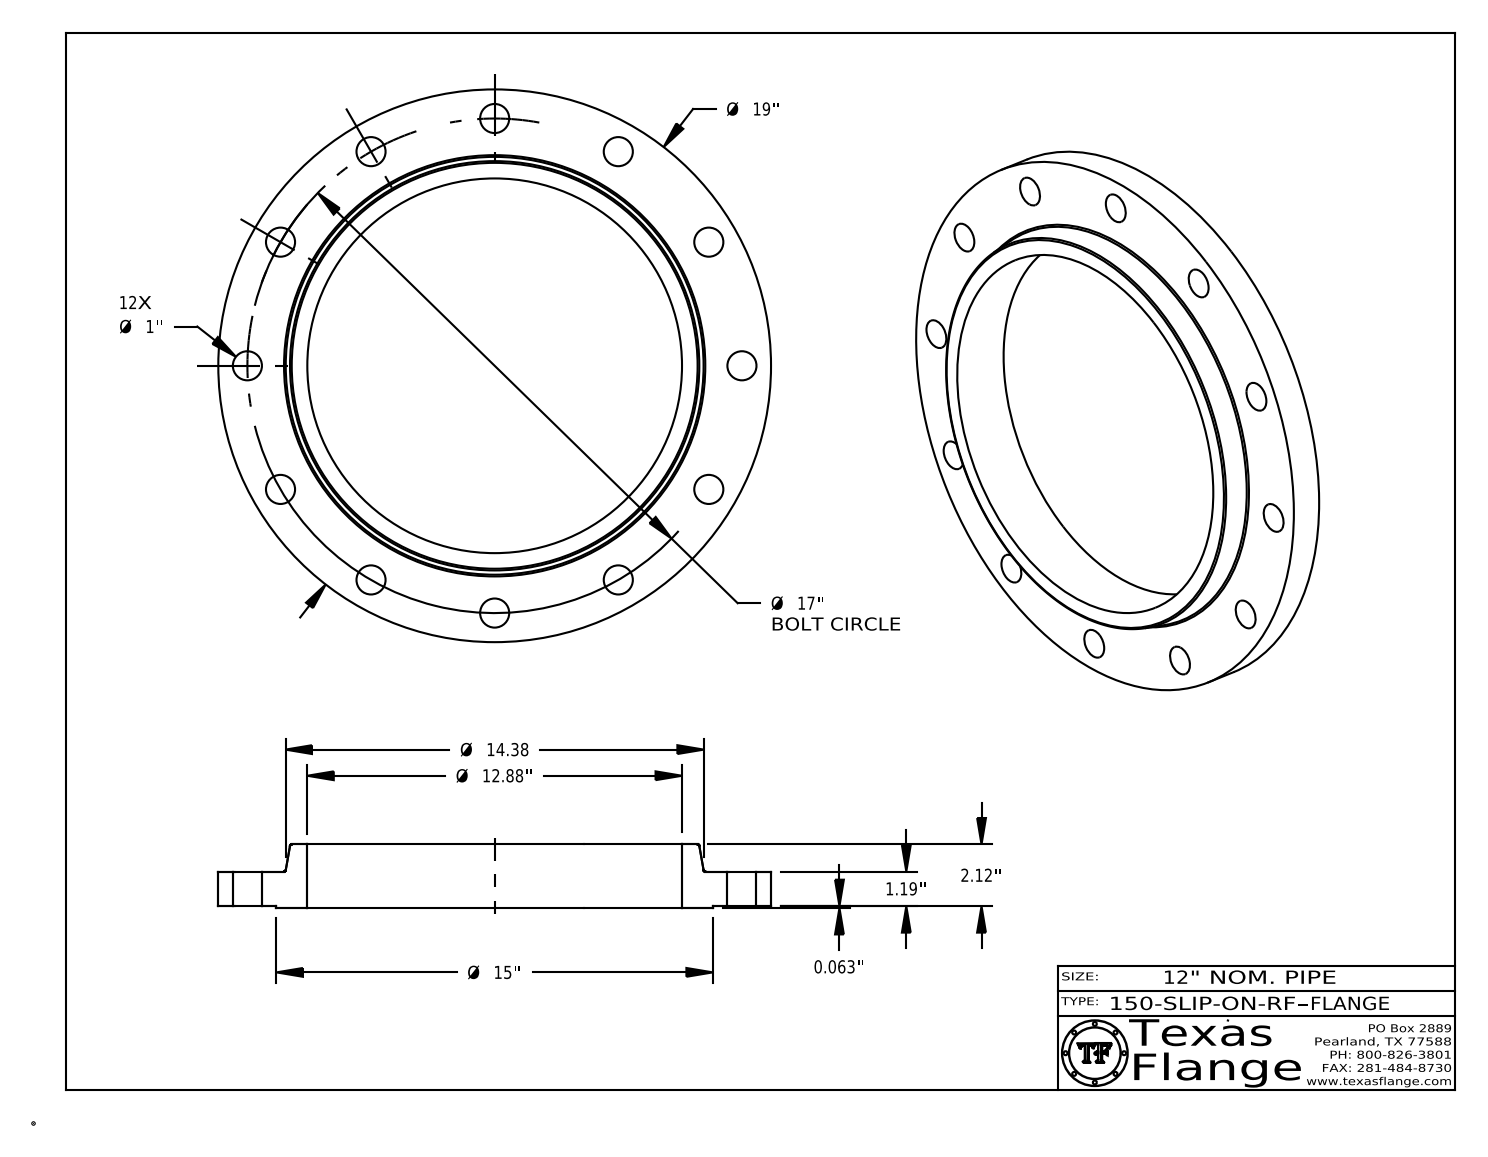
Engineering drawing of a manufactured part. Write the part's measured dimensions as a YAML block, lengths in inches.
part_name: "150-SLIP-ON-RF"
step_written_by: "CATIA V5 STEP AP214 (AUTOMOTIVE_DESIGN)"
units: inches
bodies: {solids: 1, faces: 425, planar: 369, cylindrical: 50, other: 6}
overall_size: [19, 19, 2.183]
volume: 200.5
surface_area: 528.2
round_holes:
  - {diameter: 1, count: 12}
  - {diameter: 0.495, count: 1}
  - {diameter: 12.88, count: 1}
round_bosses_or_shafts:
  - {diameter: 0.03, count: 8}
  - {diameter: 19, count: 1}
  - {diameter: 15, count: 1}
  - {diameter: 0.39, count: 1}
face_to_face_distances: [1.19, 0.063, 1.253, 2.183, 2.12, 0.93, 0.015, 1.237, 1.175, 0.945]
hole_center_spacings: [8.5, 16.42, 4.4, 12.02, 14.722, 4.4, 12.021, 14.722]
